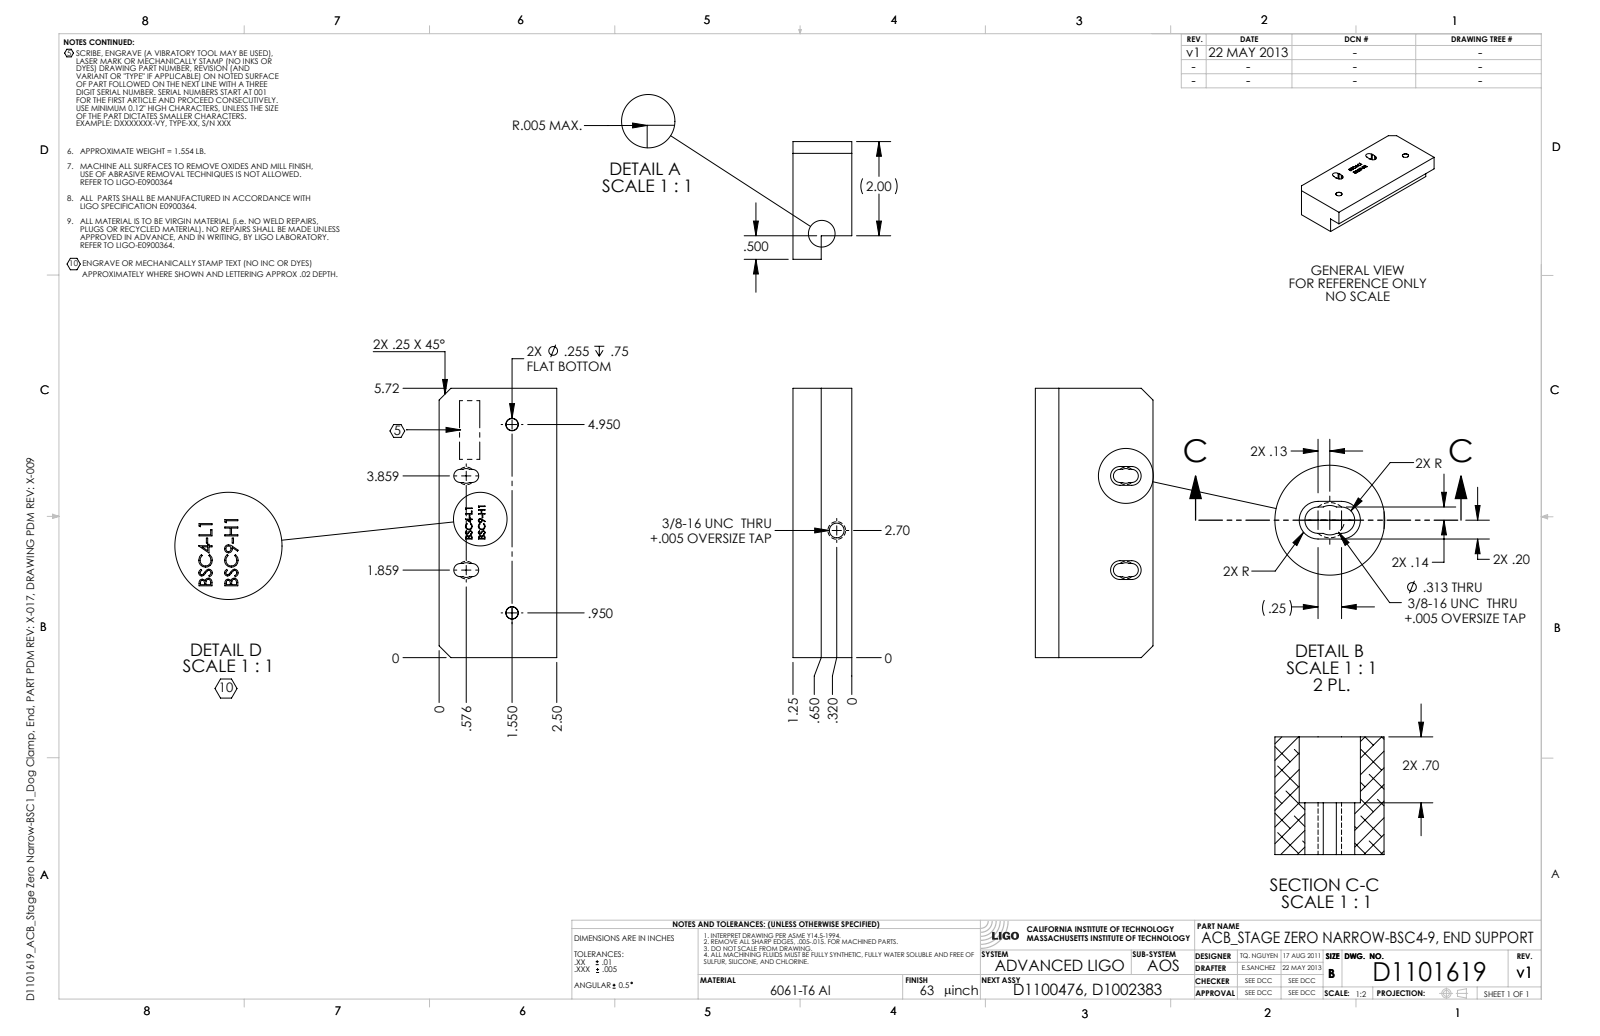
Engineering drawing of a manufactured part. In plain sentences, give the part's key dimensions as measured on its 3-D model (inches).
The part is named "D1101619-v1". Its 3-D file was written by "SolidWorks 2013 (AUTOMOTIVE_DESIGN)". It is 1 solid with 73 faces: 44 planar, 21 cylindrical and 8 other. Overall it measures 5.72 by 2.5 by 1.25 inches. Its volume is 15.24 cubic inches and its surface area 54.47 square inches. Round holes: 2 of diameter 0.255, 1 of diameter 0.313. Partial cylindrical surfaces (rounded edges, fillets, slot ends): 4 of radius 0.14, 4 of radius 0.2, 2 of radius 0.156, 1 of radius 0.005. The main face-to-face distances are 1.25, 2, 2.5, 0.5, 0.65, 0.6, 5.72, 0.4, 0.7, 0.05. The hole center spacings are 4.
